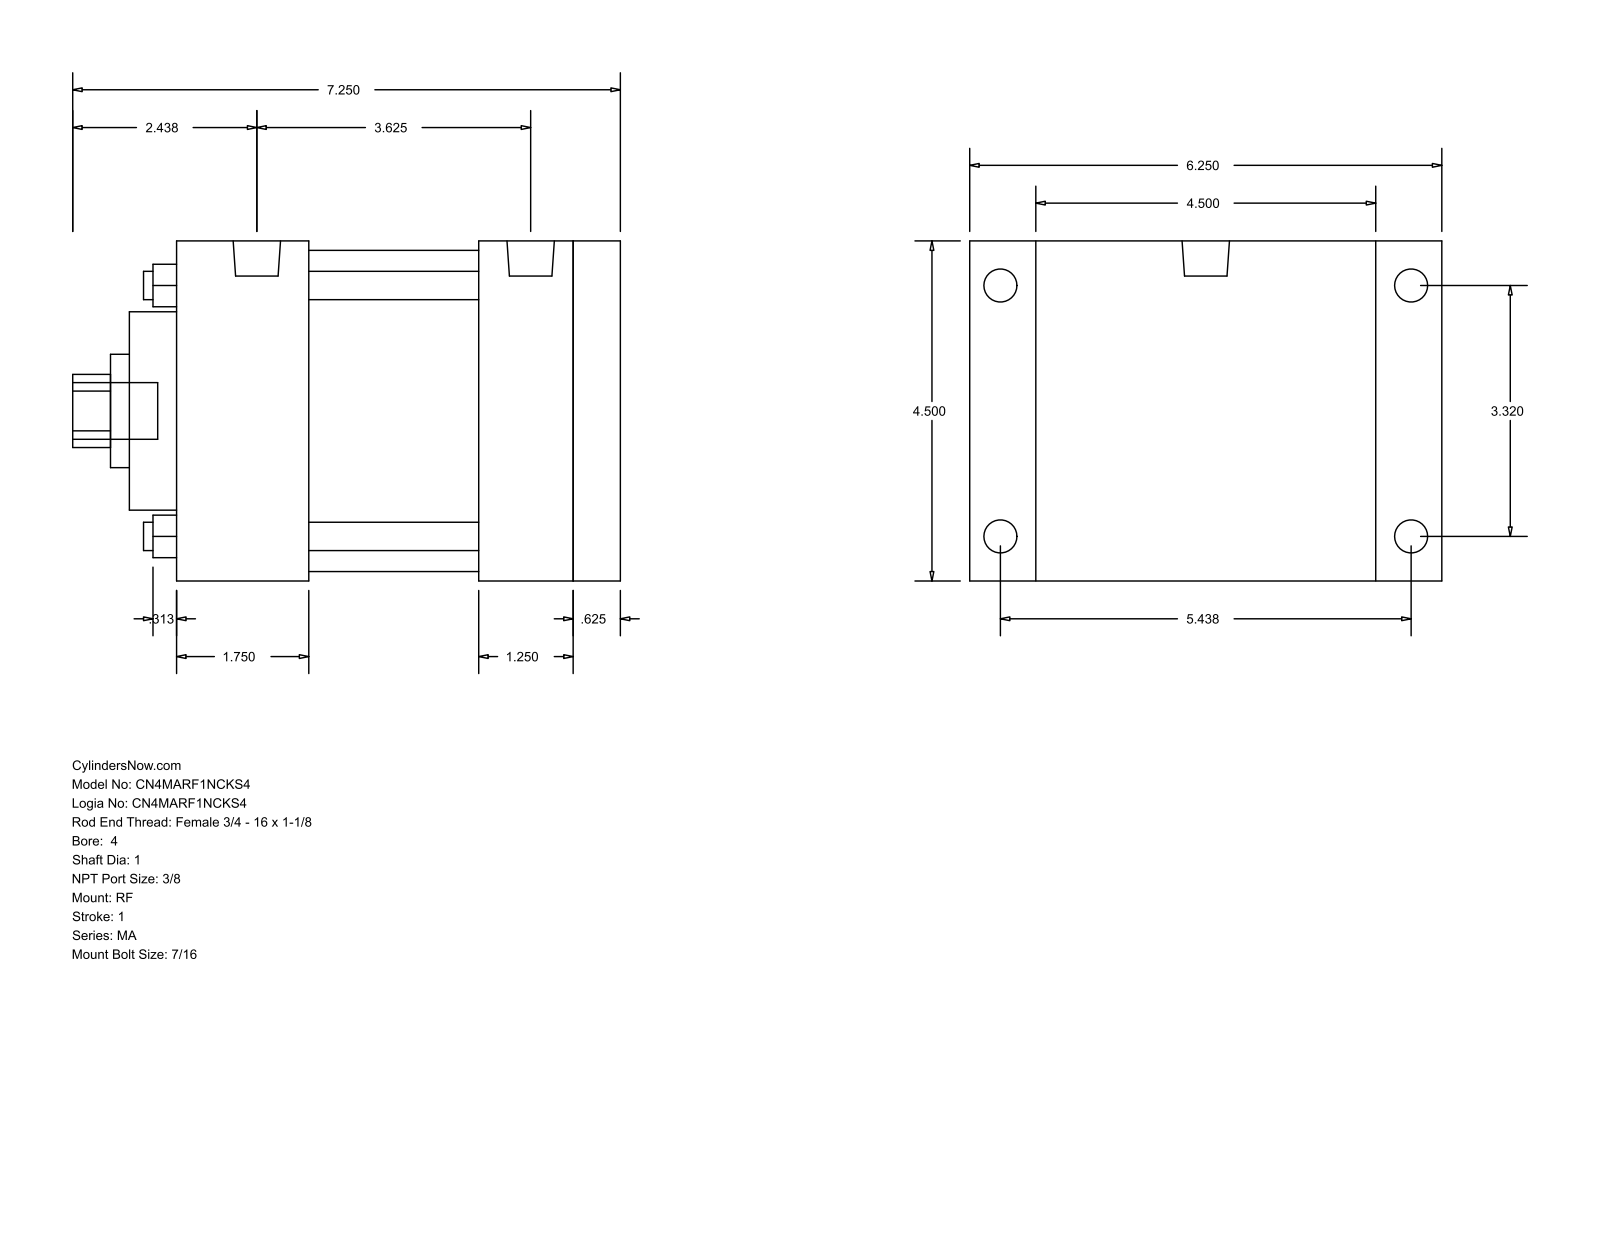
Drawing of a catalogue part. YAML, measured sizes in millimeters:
part_name: "MA_RF__0400_1"
step_written_by: "GSSL Pune (CONFIG_CONTROL_DESIGN)"
units: millimeters
bodies: {solids: 0, faces: 94, planar: 65, cylindrical: 29, other: 0}
overall_size: [184.15, 158.75, 114.3]
round_holes:
  - {diameter: 9.53, count: 4}
  - {diameter: 25.4, count: 1}
  - {diameter: 38.1, count: 1}
  - {diameter: 66.67, count: 1}
  - {diameter: 107.95, count: 1}
round_bosses_or_shafts:
  - {diameter: 11.11, count: 8}
  - {diameter: 15.93, count: 2}
  - {diameter: 19.05, count: 1}
partial_cylinders:
  - {radius: 12.29, count: 1}
face_to_face_distances: [114.3, 149.23, 15.87, 133.36, 136.53, 22.23, 101.61, 31.75, 47.62, 44.46]
hole_center_spacings: [59.62, 84.32, 119.25]
